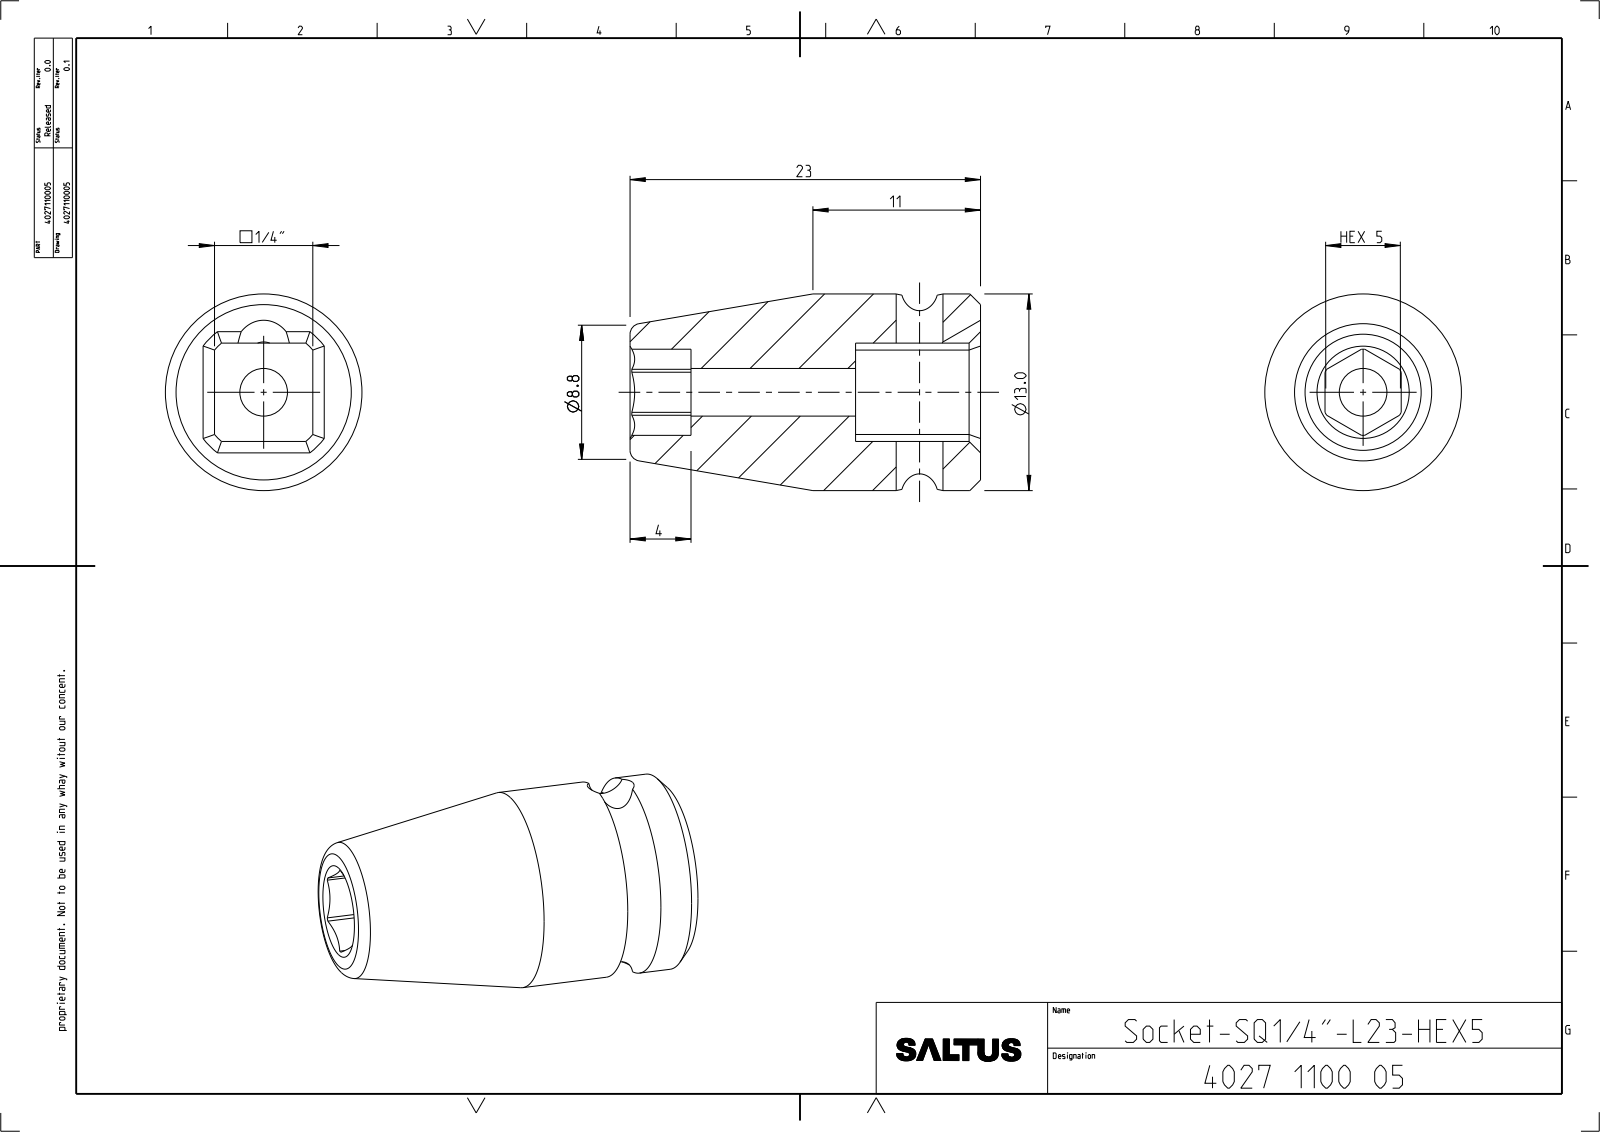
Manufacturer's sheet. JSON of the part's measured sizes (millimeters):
{"part_name": "4027110005", "step_written_by": "CREO PARAMETRIC BY PTC INC, 2022414 (CONFIG_CONTROL_DESIGN)", "units": "millimeters", "bodies": {"solids": 1, "faces": 54, "planar": 19, "cylindrical": 21, "other": 14}, "overall_size": [23, 12.9, 12.9], "volume_mm3": 1934, "surface_area_mm2": 1420, "round_holes": [[3.07, 1], [3.12, 1]], "round_bosses_or_shafts": [[12.9, 1]], "partial_cylinders_radius": [[2, 1], [2.83, 1], [4.25, 1]], "face_to_face_distances": [6.46, 8.2, 5, 0.73, 5.73, 23, 14.8, 19, 10.8, 4]}
